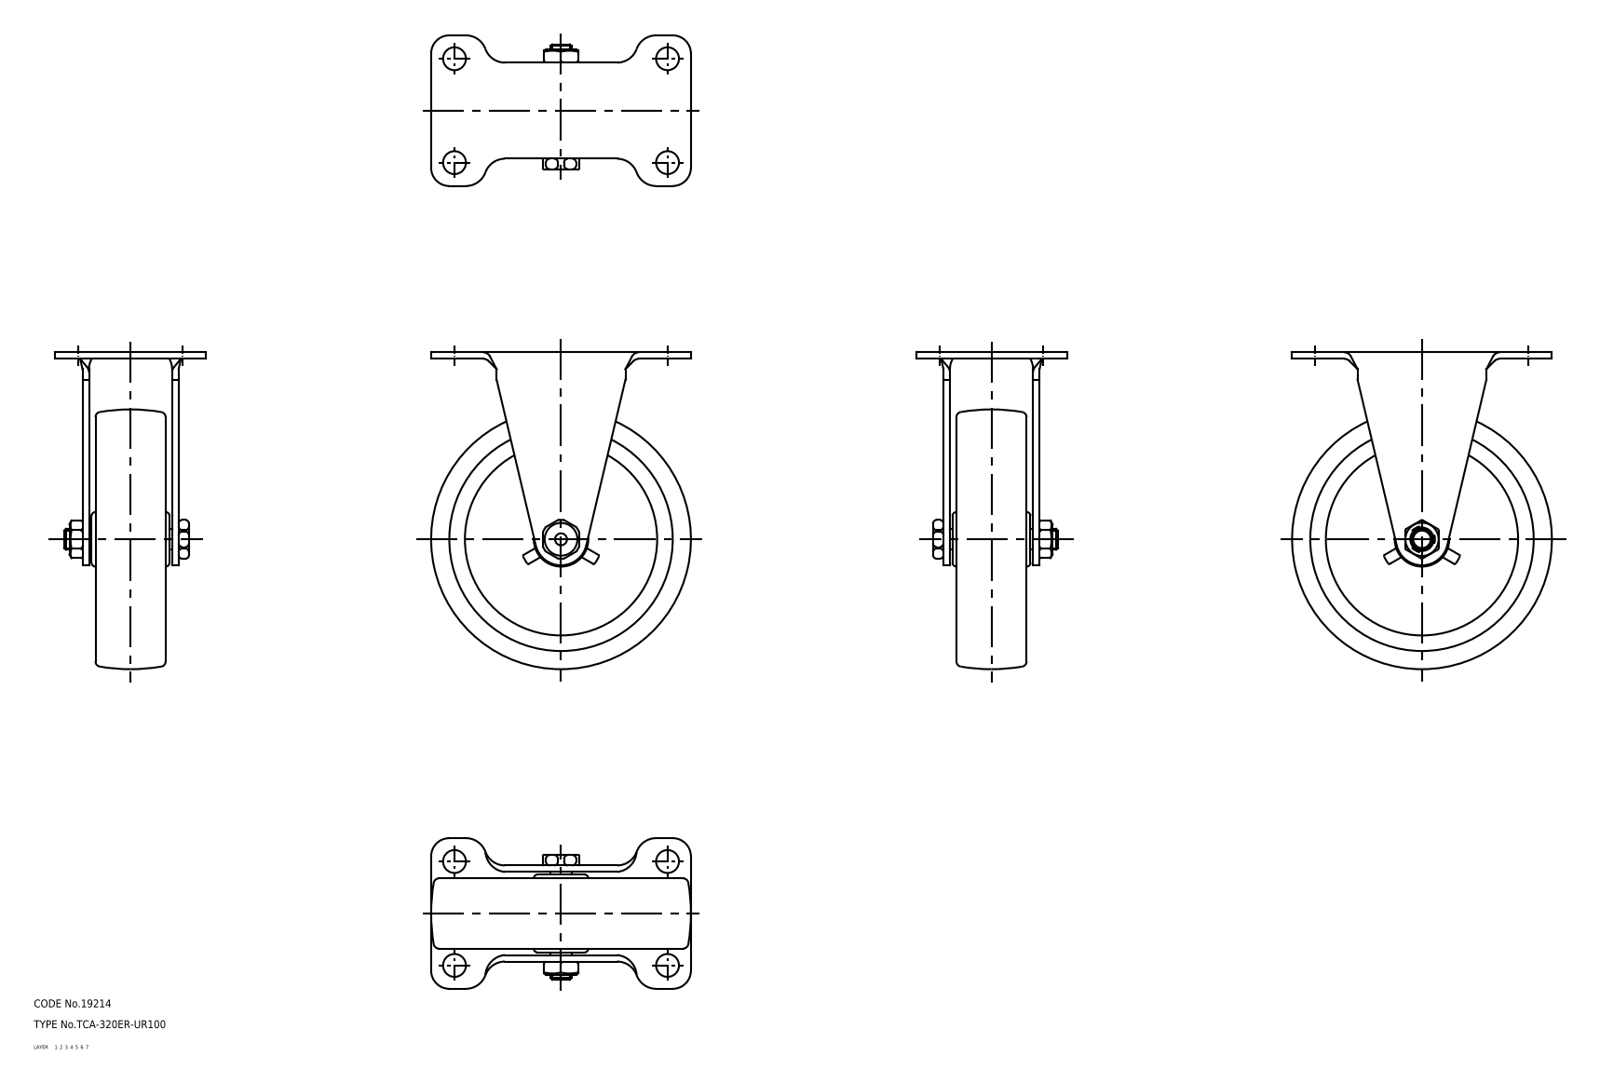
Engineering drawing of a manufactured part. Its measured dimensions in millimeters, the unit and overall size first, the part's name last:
Units: millimetres
Overall size (bounding box): 122 × 100 × 58
Volume: 186 981 mm³ · Surface area: 49 390 mm²
Bodies: 3 solids, 277 faces (0 planar, 0 cylindrical, 277 other)
Part name (STEP PRODUCT): wheel; axle; 320ER_UR100_3492_36
STEP written by: CADfix (AUTOMOTIVE_DESIGN)
